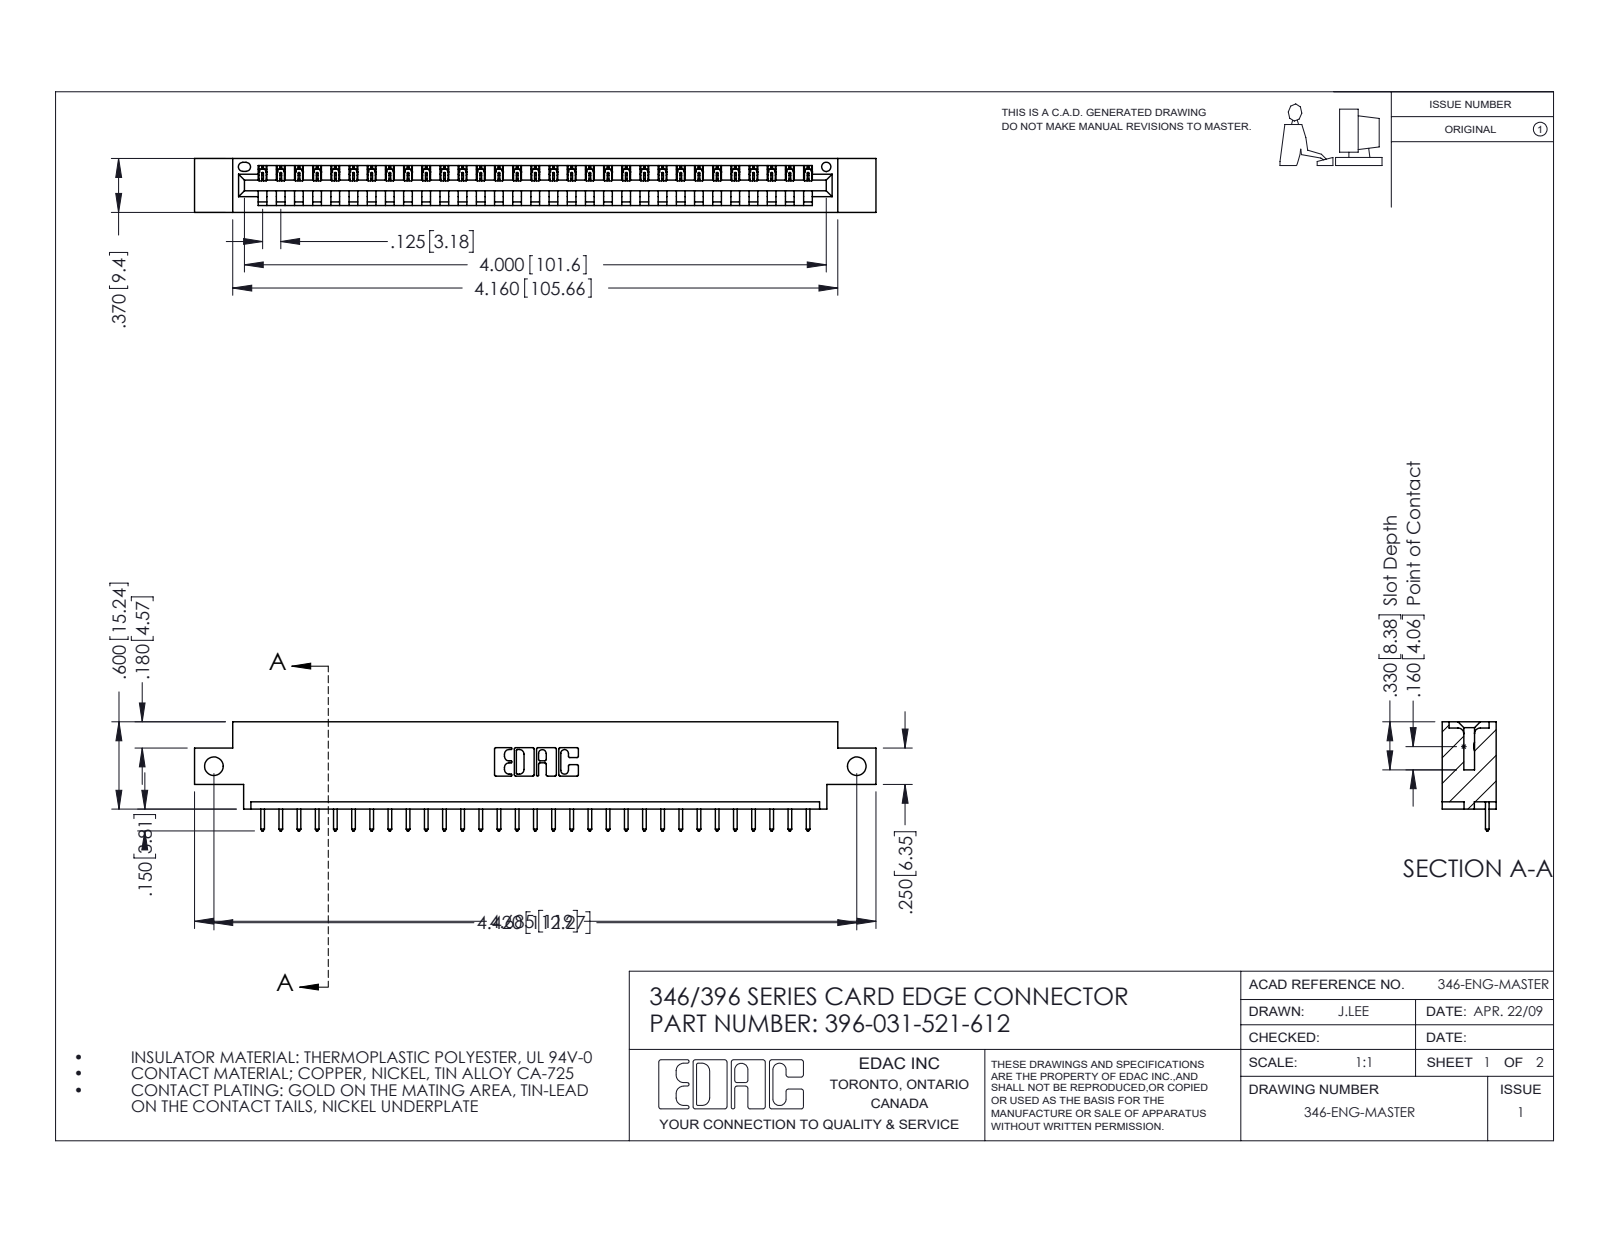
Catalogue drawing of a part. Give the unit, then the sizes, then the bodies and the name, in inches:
Units: inches
Overall size (bounding box): 4.685 × 0.75 × 0.37
Round holes (diameter × count): ⌀0.128 ×2, ⌀0.064 ×1
Partial cylindrical surfaces — rounded edges, fillets, slot ends (radius × count): R0.006 ×62, R0.01 ×62, R0.01 ×22, R0.007 ×6, R0.031 ×6, R0.026 ×3, R0.031 ×2, R0.04 ×2
Main face-to-face distances: 0.048, 0.322, 0.37, 0.25, 0.072, 0.298, 0.025, 0.148, 0.222, 0.1
Hole centre spacings: 4.42
Volume: 0.67 in³ · Surface area: 20.58 in²
Bodies: 32 solids, 1924 faces (1320 planar, 604 cylindrical, 0 other)
Part name (STEP PRODUCT): 346 Part_0.170 Offset - Side Mount; 345-292-001_345-293-121; 396-031-521-612
STEP written by: SolidWorks 2016 (CONFIG_CONTROL_DESIGN)
